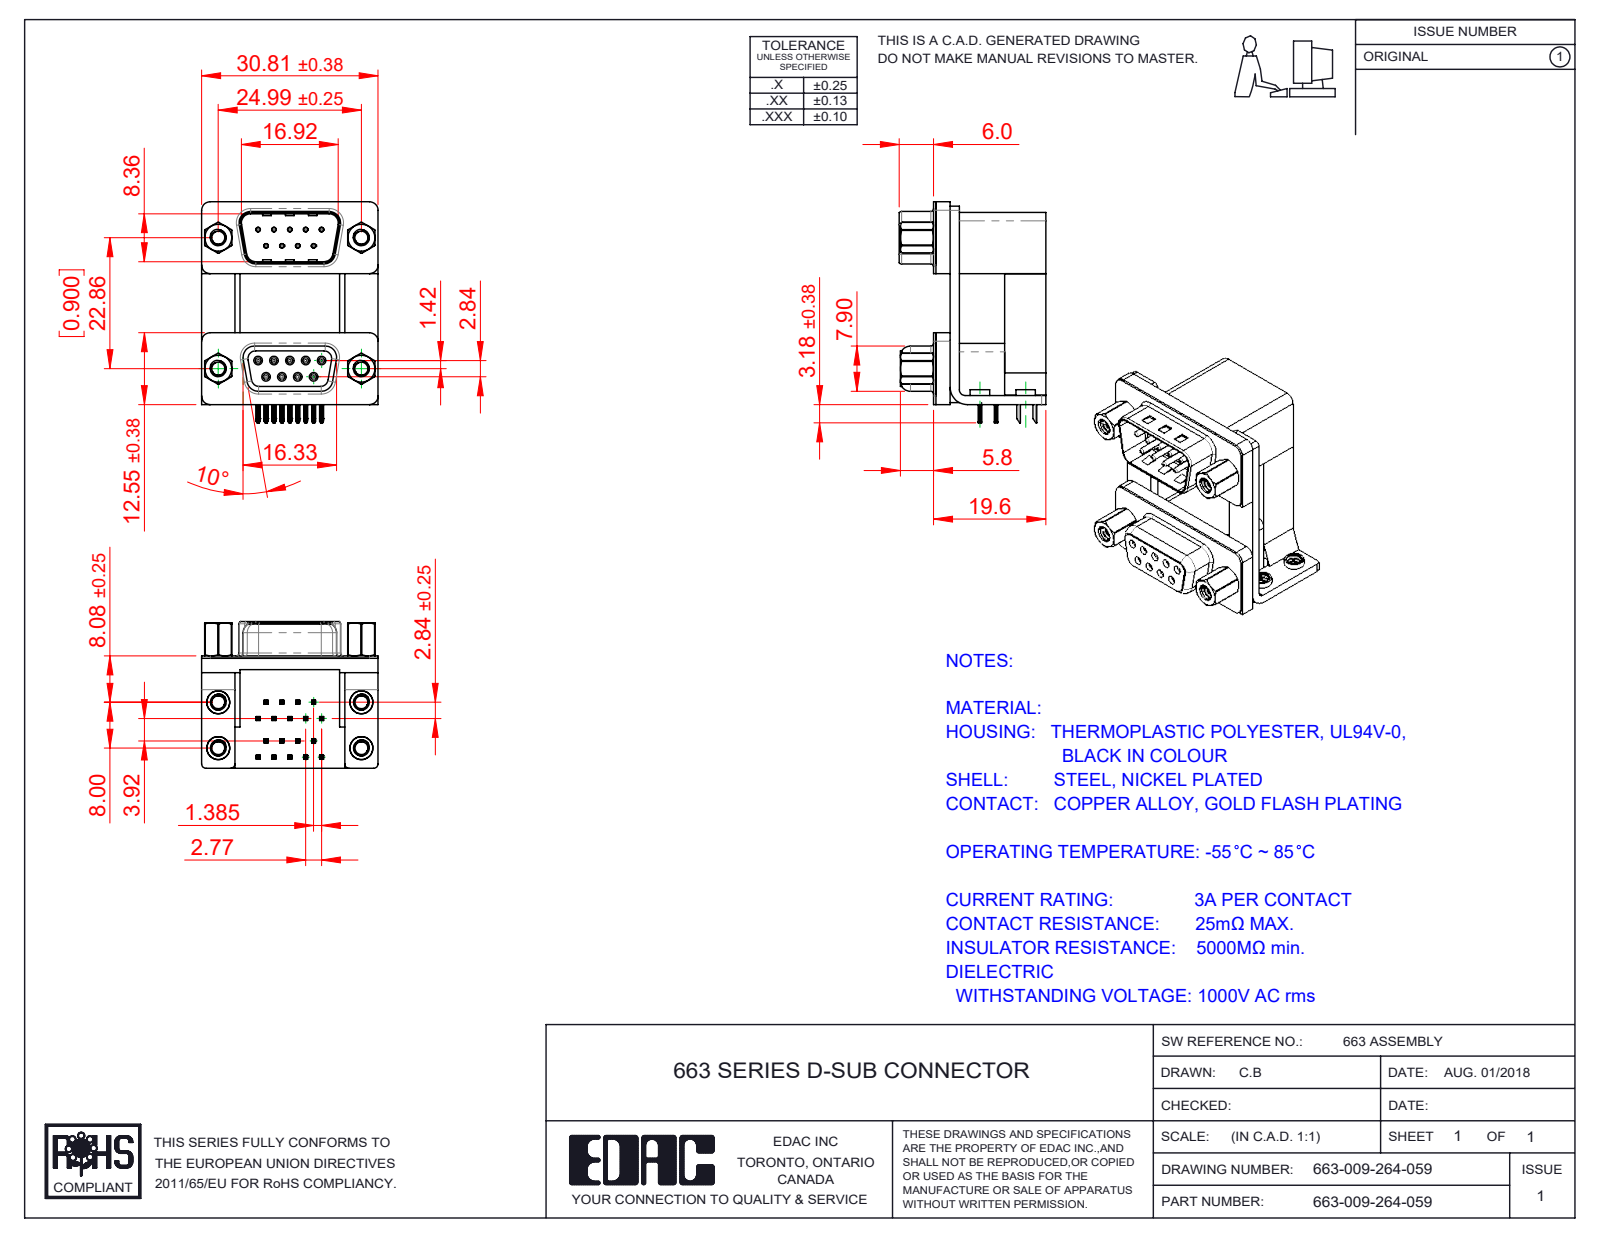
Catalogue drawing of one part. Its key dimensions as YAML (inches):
part_name: "663 Contact Top Lower; 663 Contact Bottom Upper_H; 663 Threaded Rivet_4-40; 663 Shell Plug_09 Contacts (+8 more)"
step_written_by: "SolidWorks 2020 (CONFIG_CONTROL_DESIGN)"
units: inches
bodies: {solids: 37, faces: 2921, planar: 1319, cylindrical: 915, other: 687}
overall_size: [1.519, 1.213, 1.008]
volume: 0.721
surface_area: 22.04
round_holes:
  - {diameter: 0.031, count: 18}
  - {diameter: 0.014, count: 9}
  - {diameter: 0.035, count: 9}
  - {diameter: 0.089, count: 8}
  - {diameter: 0.09, count: 4}
  - {diameter: 0.108, count: 4}
  - {diameter: 0.126, count: 4}
  - {diameter: 0.138, count: 4}
  - {diameter: 0.157, count: 4}
  - {diameter: 0.189, count: 4}
  - {diameter: 0.197, count: 4}
round_bosses_or_shafts:
  - {diameter: 0.047, count: 9}
  - {diameter: 0.03, count: 9}
  - {diameter: 0.193, count: 4}
  - {diameter: 0.187, count: 4}
  - {diameter: 0.157, count: 4}
  - {diameter: 0.154, count: 4}
  - {diameter: 0.134, count: 4}
  - {diameter: 0.11, count: 4}
partial_cylinders:
  - {radius: 0.004, count: 72}
  - {radius: 0.006, count: 36}
  - {radius: 0.01, count: 36}
  - {radius: 0.005, count: 18}
  - {radius: 0.014, count: 18}
  - {radius: 0.059, count: 15}
  - {radius: 0.02, count: 12}
  - {radius: 0.013, count: 9}
face_to_face_distances: [0.016, 0.098, 0.657, 0.756, 0.472, 0.283, 0.374, 0.488, 0.063, 0.772]
hole_center_spacings: [0.124, 0.109, 0.907, 0.9, 0.218, 0.926, 0.79, 1.013]
